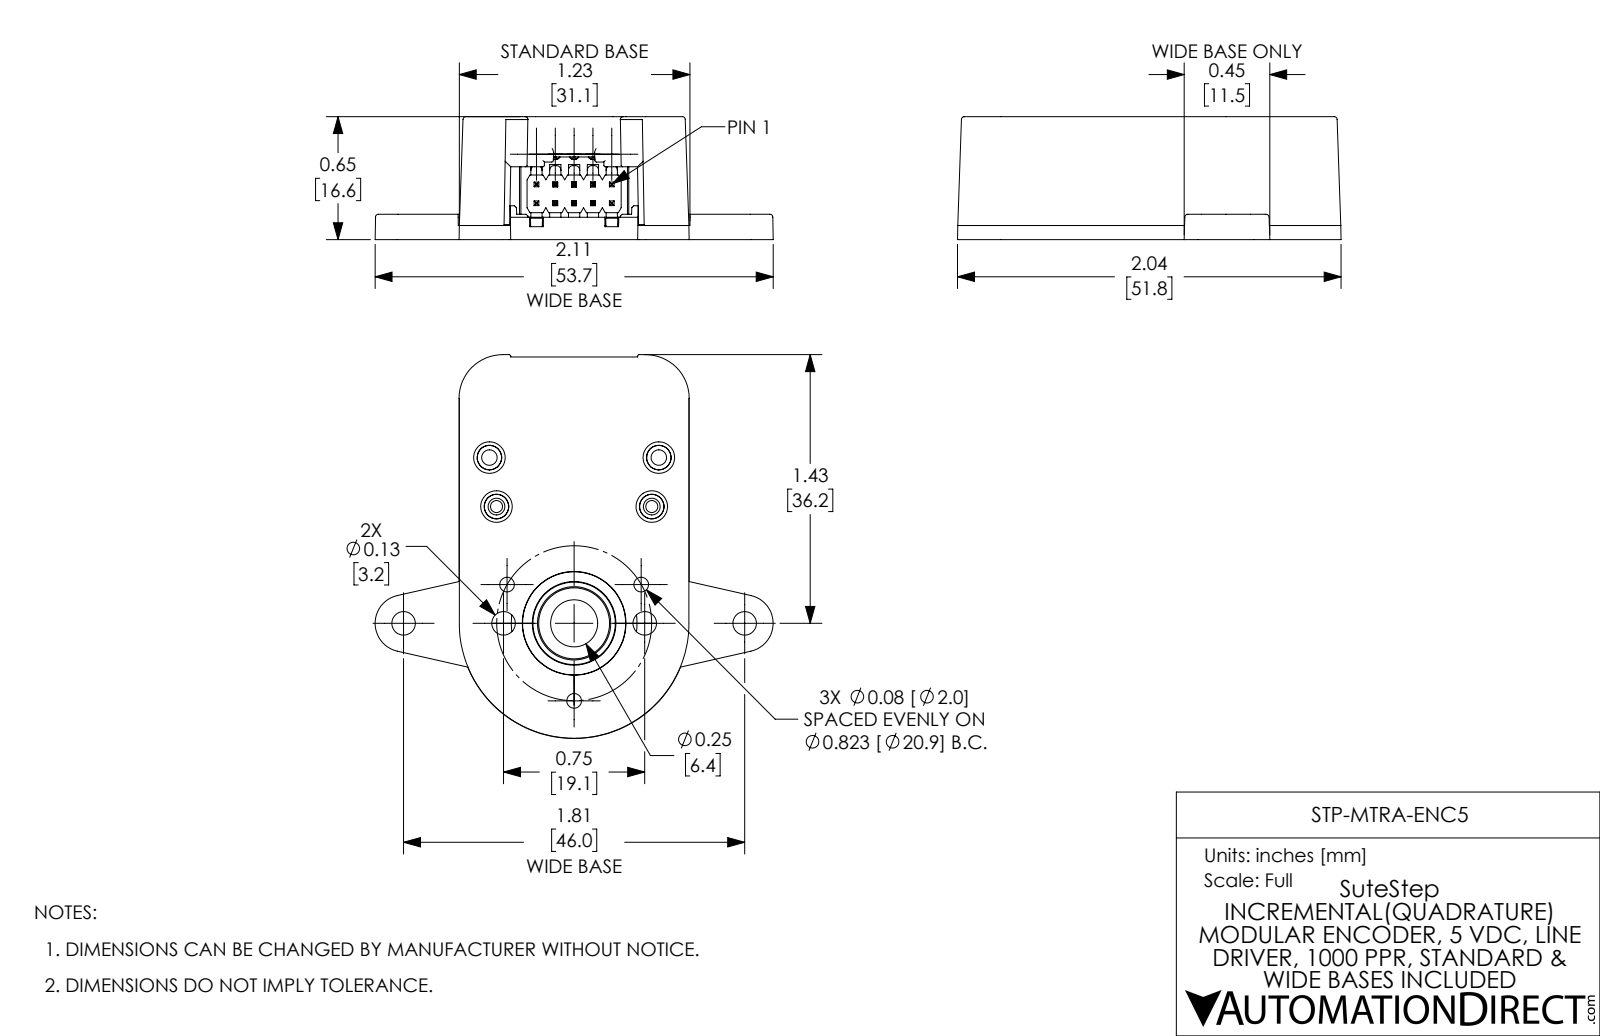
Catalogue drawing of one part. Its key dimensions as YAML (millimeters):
part_name: "STP-MTRA-ENC5"
step_written_by: "SolidWorks 2017 (AUTOMOTIVE_DESIGN)"
units: millimeters
bodies: {solids: 32, faces: 2929, planar: 1428, cylindrical: 762, other: 739}
overall_size: [91.1, 53.6, 16.6]
volume: 19620
surface_area: 20650
round_holes:
  - {diameter: 3.3, count: 8}
  - {diameter: 2, count: 6}
  - {diameter: 0.8, count: 5}
  - {diameter: 2.3, count: 4}
  - {diameter: 3.2, count: 4}
  - {diameter: 2.8, count: 2}
  - {diameter: 2.4, count: 1}
  - {diameter: 2.4, count: 1}
  - {diameter: 2.4, count: 1}
  - {diameter: 6.4, count: 1}
round_bosses_or_shafts:
  - {diameter: 2, count: 5}
  - {diameter: 4.7, count: 4}
  - {diameter: 4.1, count: 4}
  - {diameter: 5.6, count: 2}
  - {diameter: 5, count: 2}
  - {diameter: 2.8, count: 2}
  - {diameter: 2.7, count: 2}
  - {diameter: 25.4, count: 1}
partial_cylinders:
  - {radius: 0.6, count: 46}
  - {radius: 0.4, count: 41}
  - {radius: 0.2, count: 16}
  - {radius: 0.1, count: 14}
  - {radius: 0.8, count: 12}
  - {radius: 0.5, count: 10}
  - {radius: 0.4, count: 6}
  - {radius: 0.8, count: 6}
face_to_face_distances: [3.4, 3.2, 16.6, 16.3, 13.2, 13.7, 1.5, 2.9, 13.5, 10.3]
hole_center_spacings: [48.7, 18.1, 2.5, 10.6, 22.2, 22.4, 28.2, 5.1]
